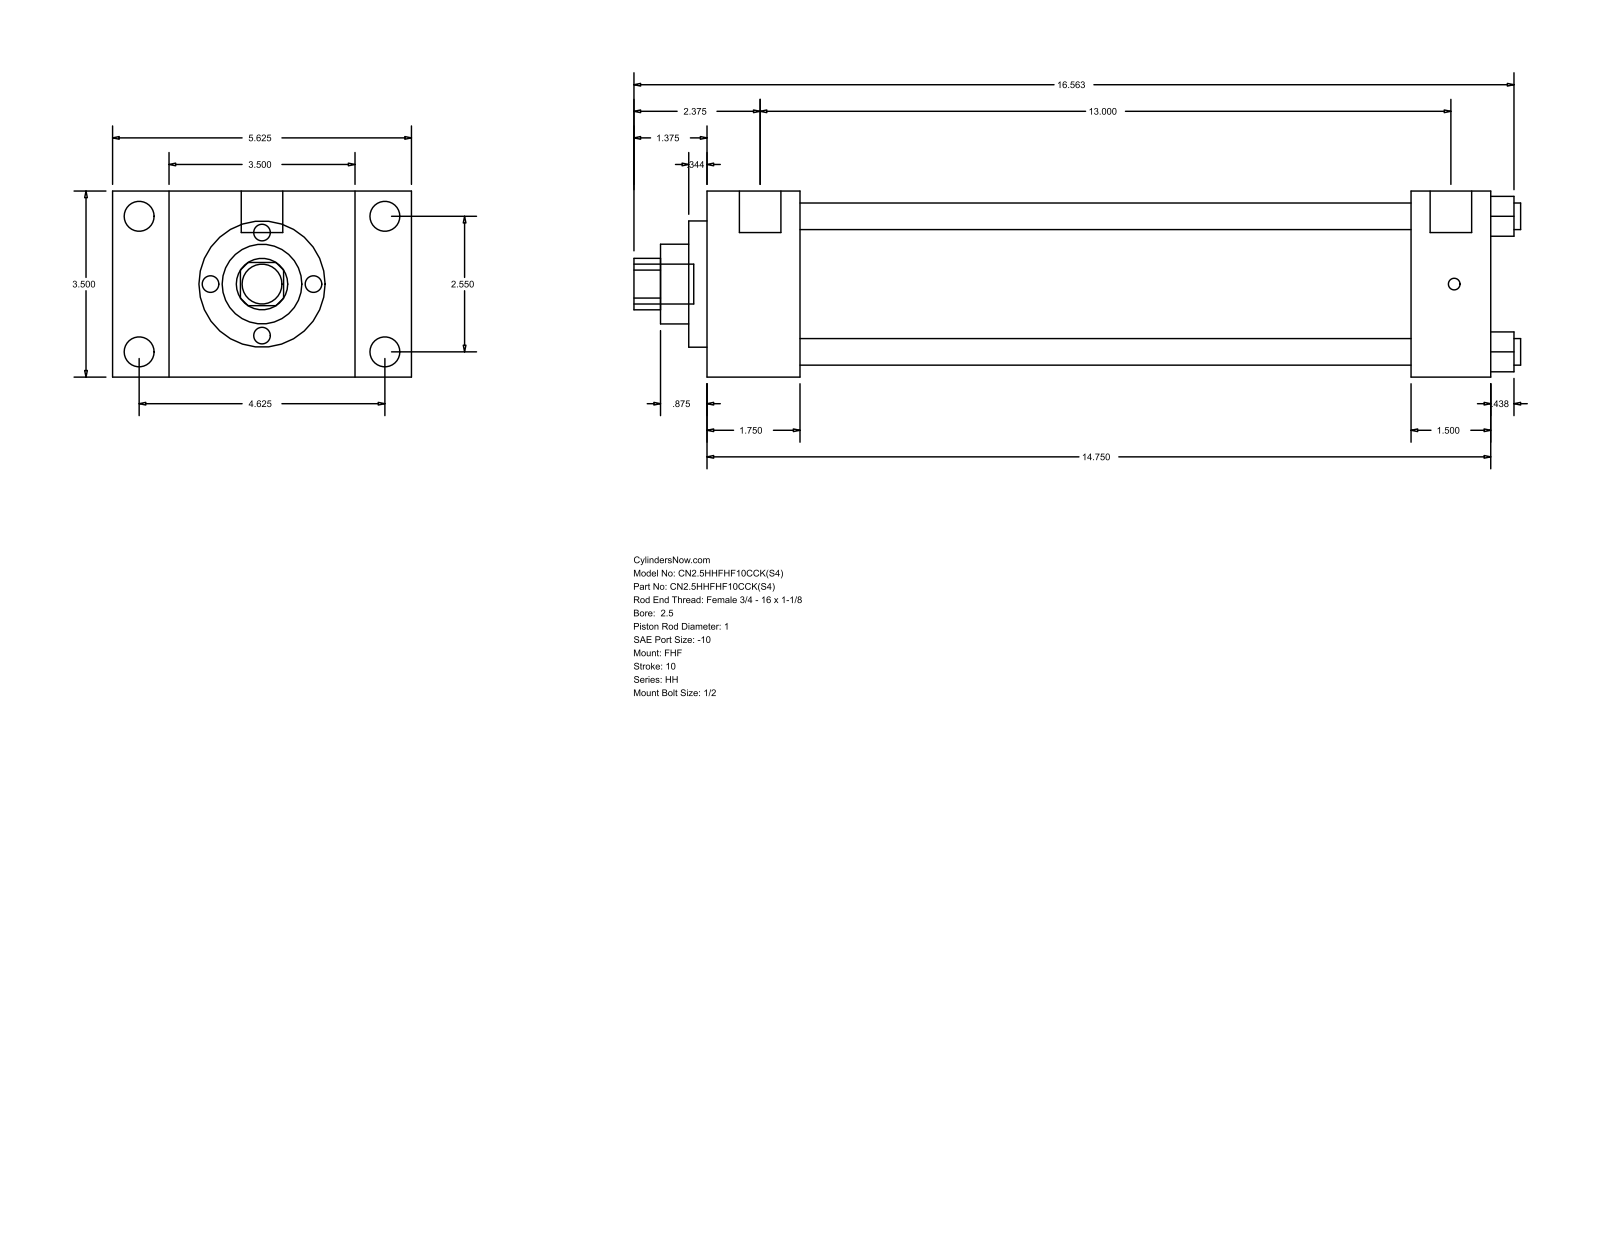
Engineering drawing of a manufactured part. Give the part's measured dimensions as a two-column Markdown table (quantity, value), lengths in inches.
| quantity | value |
| --- | --- |
| part name | HH_FHF__0250_1 |
| STEP written by | GSSL Pune (CONFIG_CONTROL_DESIGN) |
| units | inches |
| bodies | 0 solids, 90 faces (61 planar, 29 cylindrical, 0 other) |
| overall size | 16.687 × 5.625 × 3.5 |
| round holes (diameter × count) | 0.5 × 4, 1 × 1, 1.5 × 1, 2.375 × 1, 2.875 × 1 |
| round bosses / shafts (diameter × count) | 0.563 × 4, 0.219 × 4, 0.781 × 2, 0.75 × 1 |
| partial cylindrical surfaces (radius × count) | 0.484 × 1 |
| main face-to-face distances | 3.5, 1.75, 1.063, 4.563, 14.75, 13, 5.625, 13.25, 11.5, 1.5 |
| hole center spacings | 1.803, 2.55, 3.606 |
